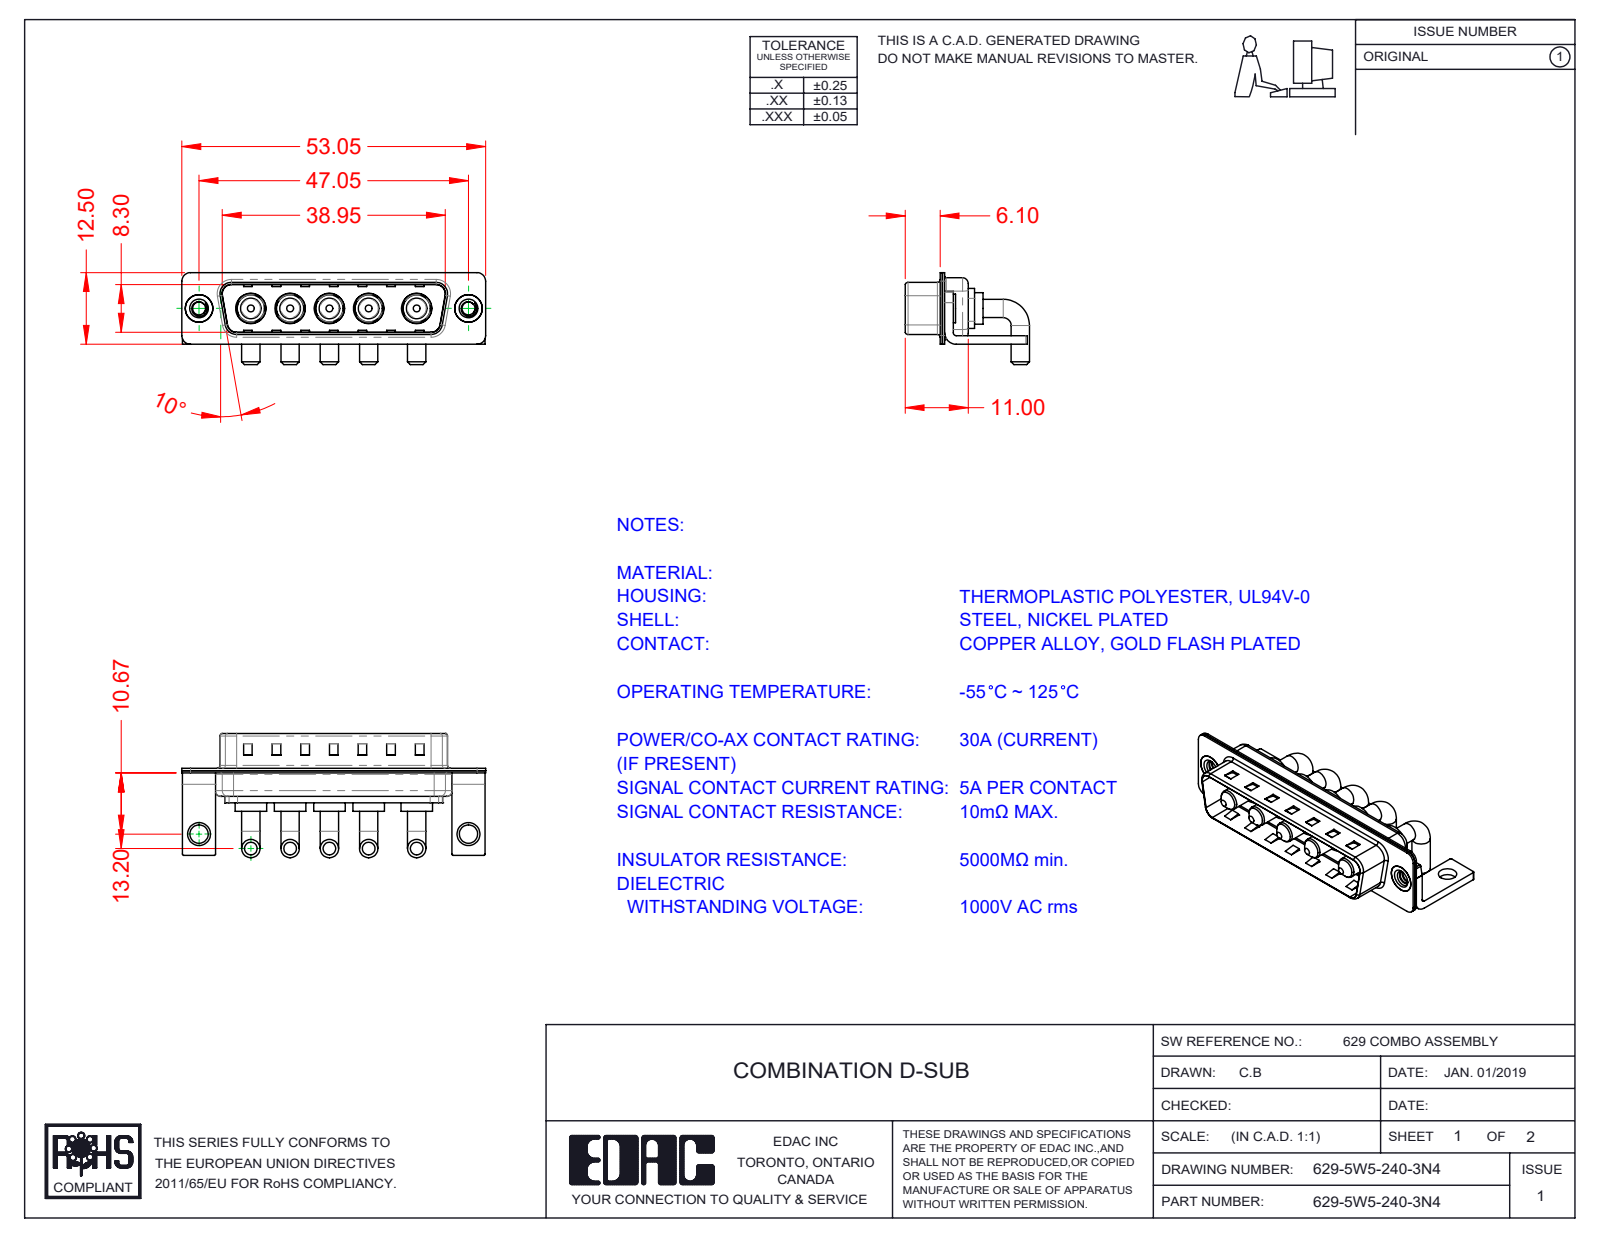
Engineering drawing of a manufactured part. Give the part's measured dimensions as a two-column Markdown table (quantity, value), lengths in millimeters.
| quantity | value |
| --- | --- |
| part name | 629Combo Housing_5W5; 629Combo Shell Rear_25 Contacts; 629Combo Threaded Rivet_3; 629-5W5-240-3N4 (+3 more) |
| STEP written by | SolidWorks 2020 (CONFIG_CONTROL_DESIGN) |
| units | millimeters |
| bodies | 17 solids, 631 faces (241 planar, 260 cylindrical, 130 other) |
| overall size | 53.05 × 21.7 × 16.05 |
| volume | 3 810 mm³ |
| surface area | 7 825 mm² |
| round holes (diameter × count) | 4.85 × 5, 5.3 × 5, 2.26 × 2, 3.2 × 2, 4 × 2, 4.8 × 2 |
| round bosses / shafts (diameter × count) | 3.2 × 10, 5.5 × 5, 5.2 × 5, 4.75 × 5, 3.75 × 5, 3.6 × 5, 5 × 2, 4.9 × 2 |
| partial cylindrical surfaces (radius × count) | 0.25 × 16, 1.5 × 16, 2 × 13, 0.5 × 9, 1.6 × 8, 2.1 × 5, 0.6 × 4, 0.65 × 4 |
| main face-to-face distances | 0.4, 0.8, 9.5, 1.5, 9.1, 8.7, 9.9, 5.2, 0.75, 1.2 |
| hole center spacings | 6.86, 13.73, 47.05, 6.85, 6.87, 8.37, 8.38, 9.04 |
